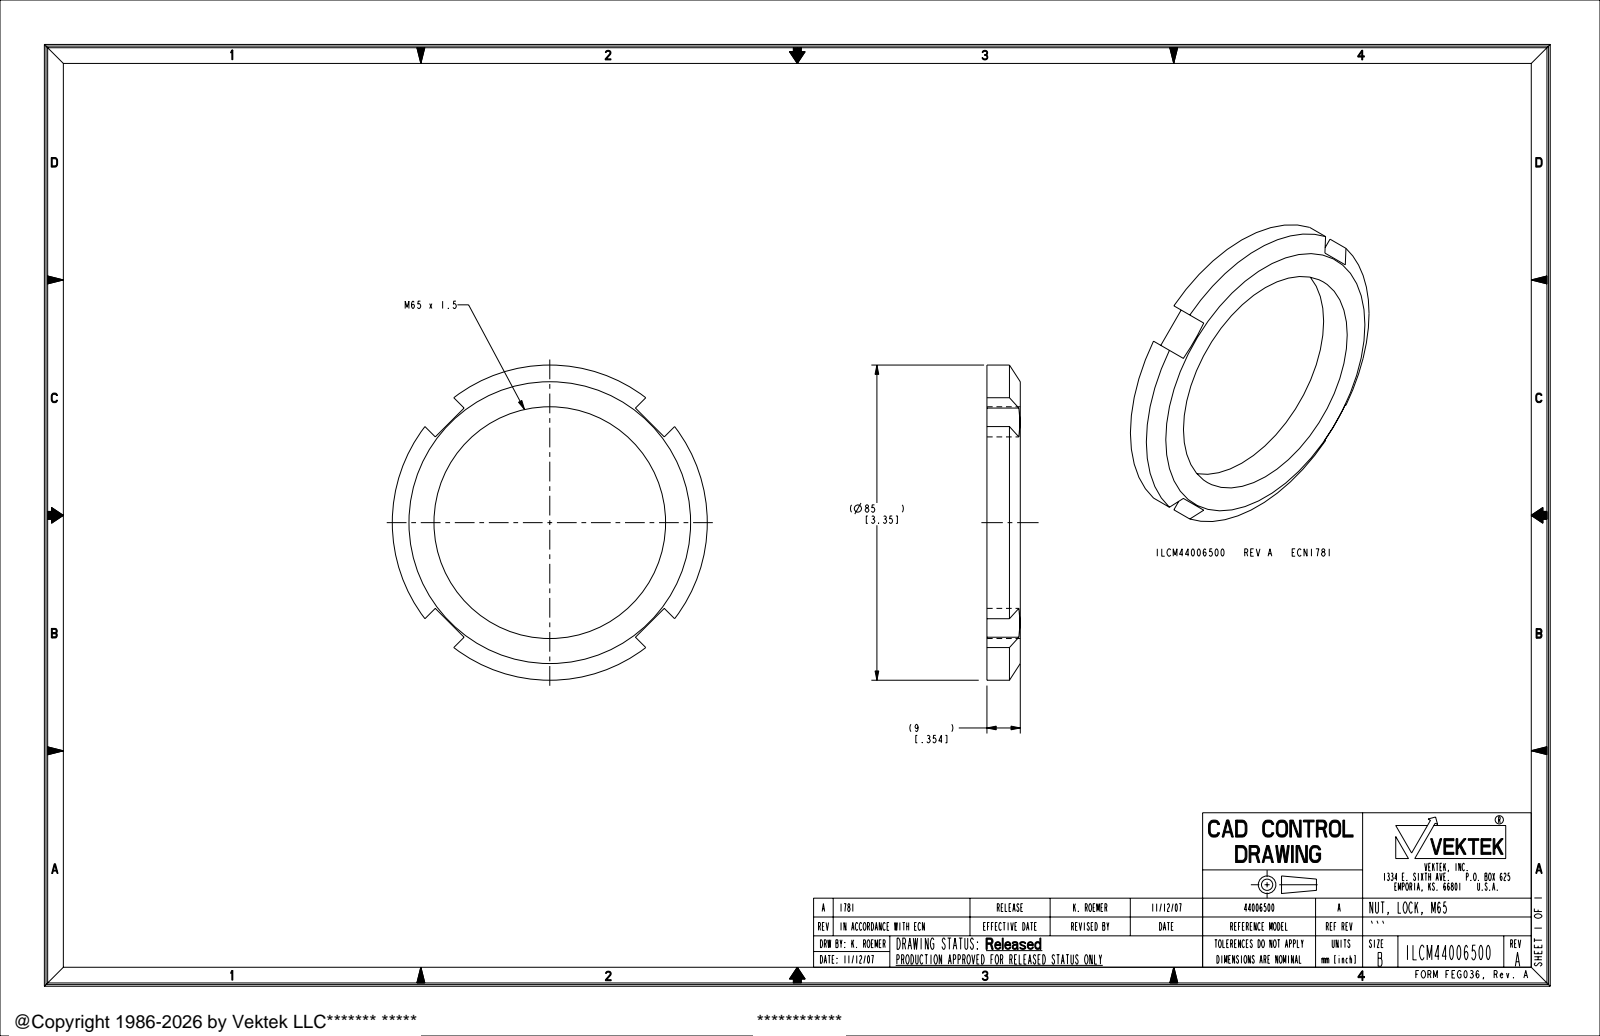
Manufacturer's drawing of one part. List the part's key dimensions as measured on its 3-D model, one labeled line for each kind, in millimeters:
Part name (STEP PRODUCT): ILCM44006500
STEP written by: PRO/ENGINEER BY PARAMETRIC TECHNOLOGY CORPORATION, 2005180 (AUTOMOTIVE_DESIGN_CC2)
Units: millimetres
Bodies: 1 solid, 22 faces (14 planar, 6 cylindrical, 2 other)
Overall size (bounding box): 85 × 85 × 9
Volume: 20 398 mm³ · Surface area: 8 769 mm²
Round holes (diameter × count): ⌀62.5 ×1
Round bosses / shafts (diameter × count): ⌀85 ×1
Main face-to-face distances: 9, 32.69, 43.69, 76.38, 11
